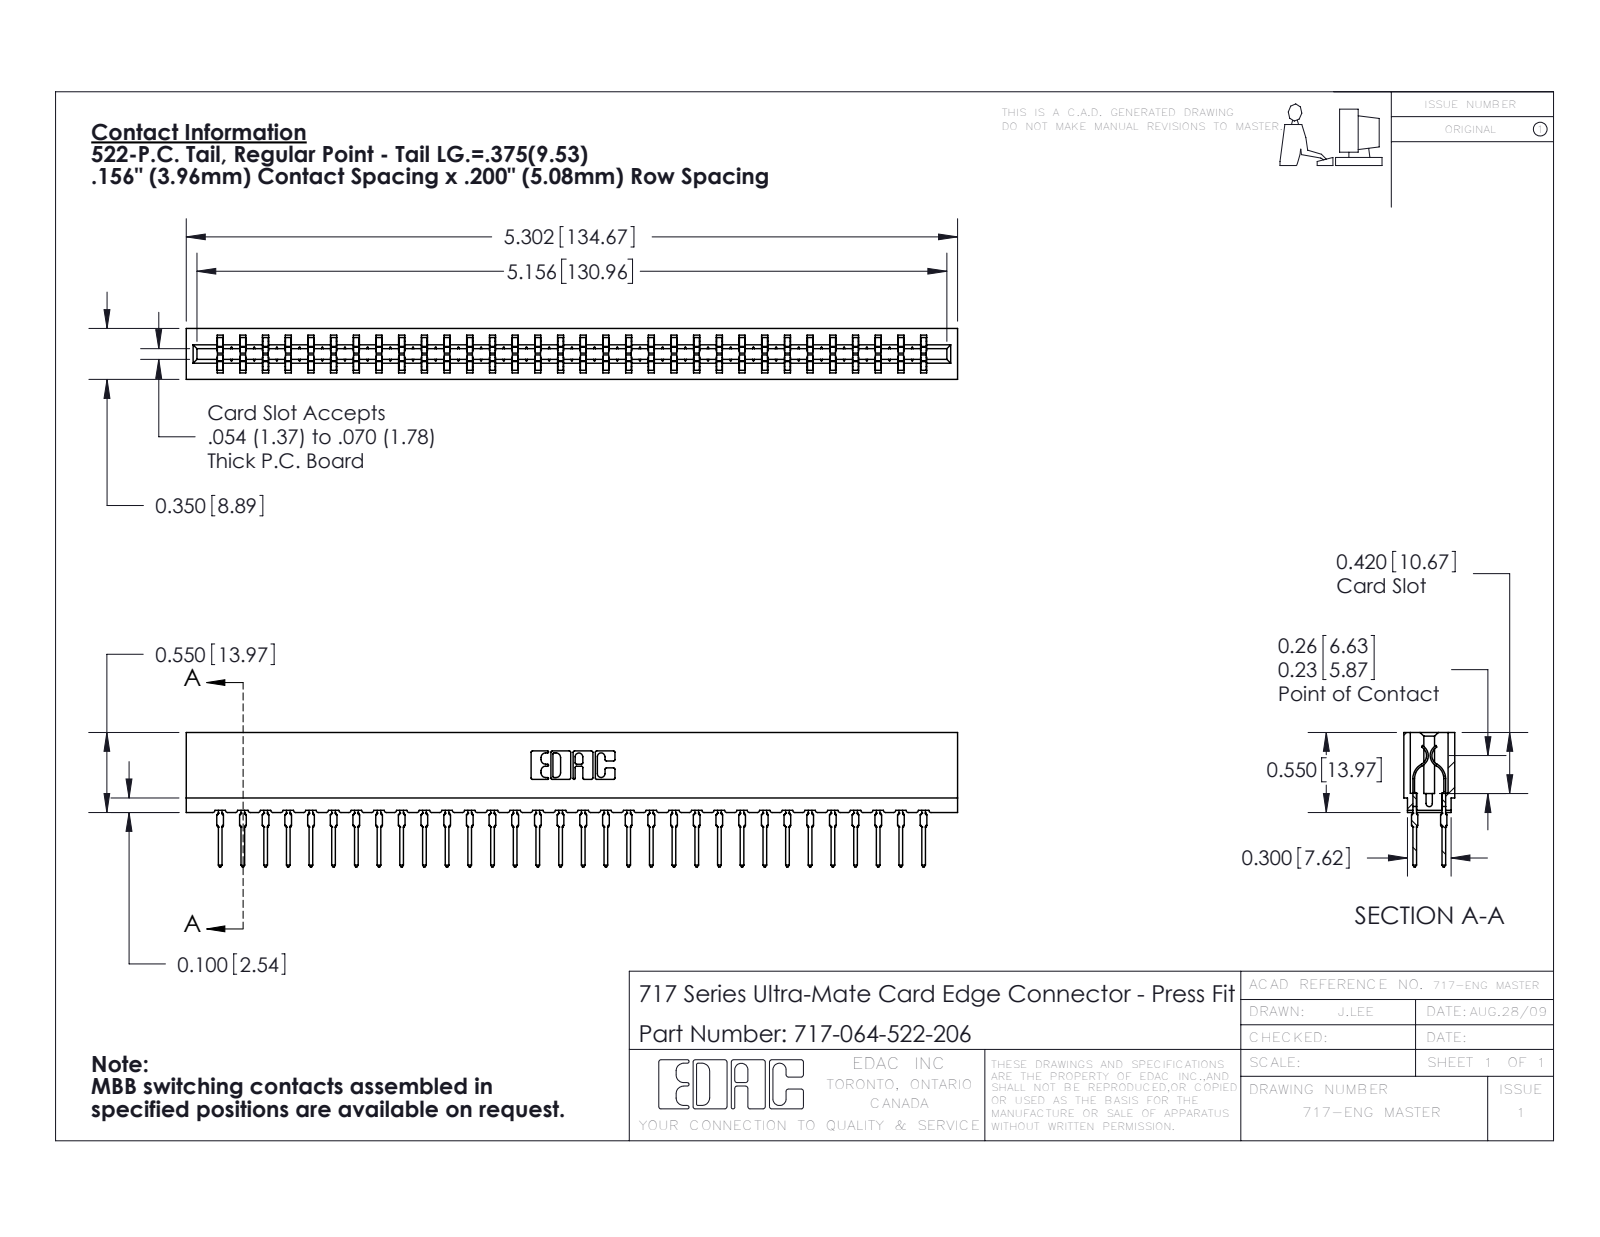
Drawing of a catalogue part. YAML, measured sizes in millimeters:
part_name: "745-292-001_522; 717 Part_Insulator Option - 06; 717-064-522-206"
step_written_by: "SolidWorks 2016 (CONFIG_CONTROL_DESIGN)"
units: millimeters
bodies: {solids: 65, faces: 5854, planar: 3030, cylindrical: 1160, other: 1664}
overall_size: [134.7, 23.5, 8.9]
volume: 11800
surface_area: 18140
partial_cylinders:
  - {radius: 0.5, count: 128}
  - {radius: 0.4, count: 64}
  - {radius: 0.3, count: 22}
  - {radius: 0.1, count: 8}
  - {radius: 0.3, count: 8}
  - {radius: 0.2, count: 6}
  - {radius: 0.8, count: 6}
  - {radius: 0.7, count: 3}
face_to_face_distances: [5.4, 3.5, 8.9, 1.6, 7.3, 1.9, 3.8, 1.9, 1.1, 7.7]
